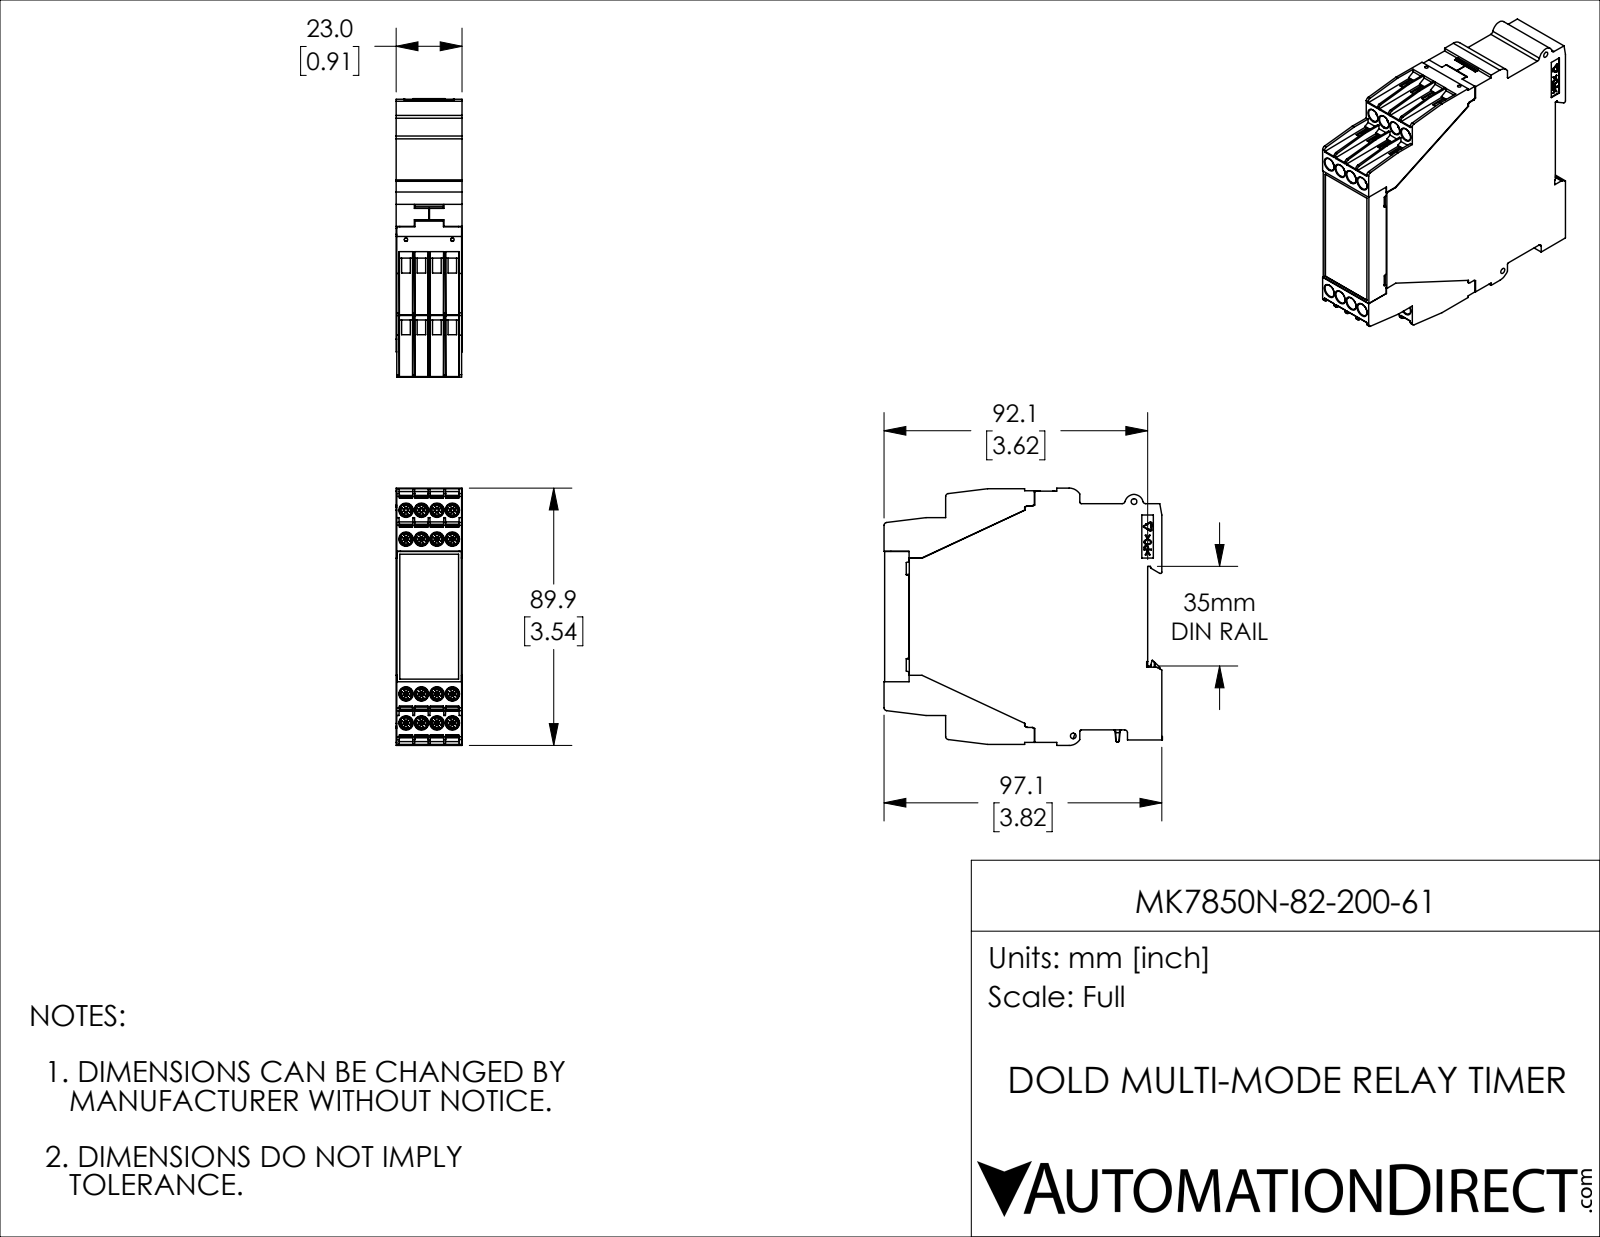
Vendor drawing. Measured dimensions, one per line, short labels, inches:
name: MK7850N-82-200-61
written by: SolidWorks 2019 (CONFIG_CONTROL_DESIGN)
unit: in
bodies: 1 solid, 1833 faces (1399 planar, 295 cylindrical, 139 other)
size: 3.827 × 3.537 × 0.906
volume: 10.38 in³; area: 51.14 in²
holes: 16× ⌀0.181, 3× ⌀0.079, 2× ⌀0.047, 2× ⌀0.079
bosses: 12× ⌀0.173, 1× ⌀0.087
rounds: 50× R0.012, 30× R0.02, 23× R0.039, 7× R0.008, 6× R0.006, 6× R0.014, 4× R0.087, 2× R0.174
face distances: 0.906, 0.9, 0.026, 0.864, 0.894, 0.035, 0.839, 0.031, 0.874, 0.868
hole spacings: 0.213, 0.451, 2.535, 0.398, 0.425, 0.582, 2.526, 2.561
